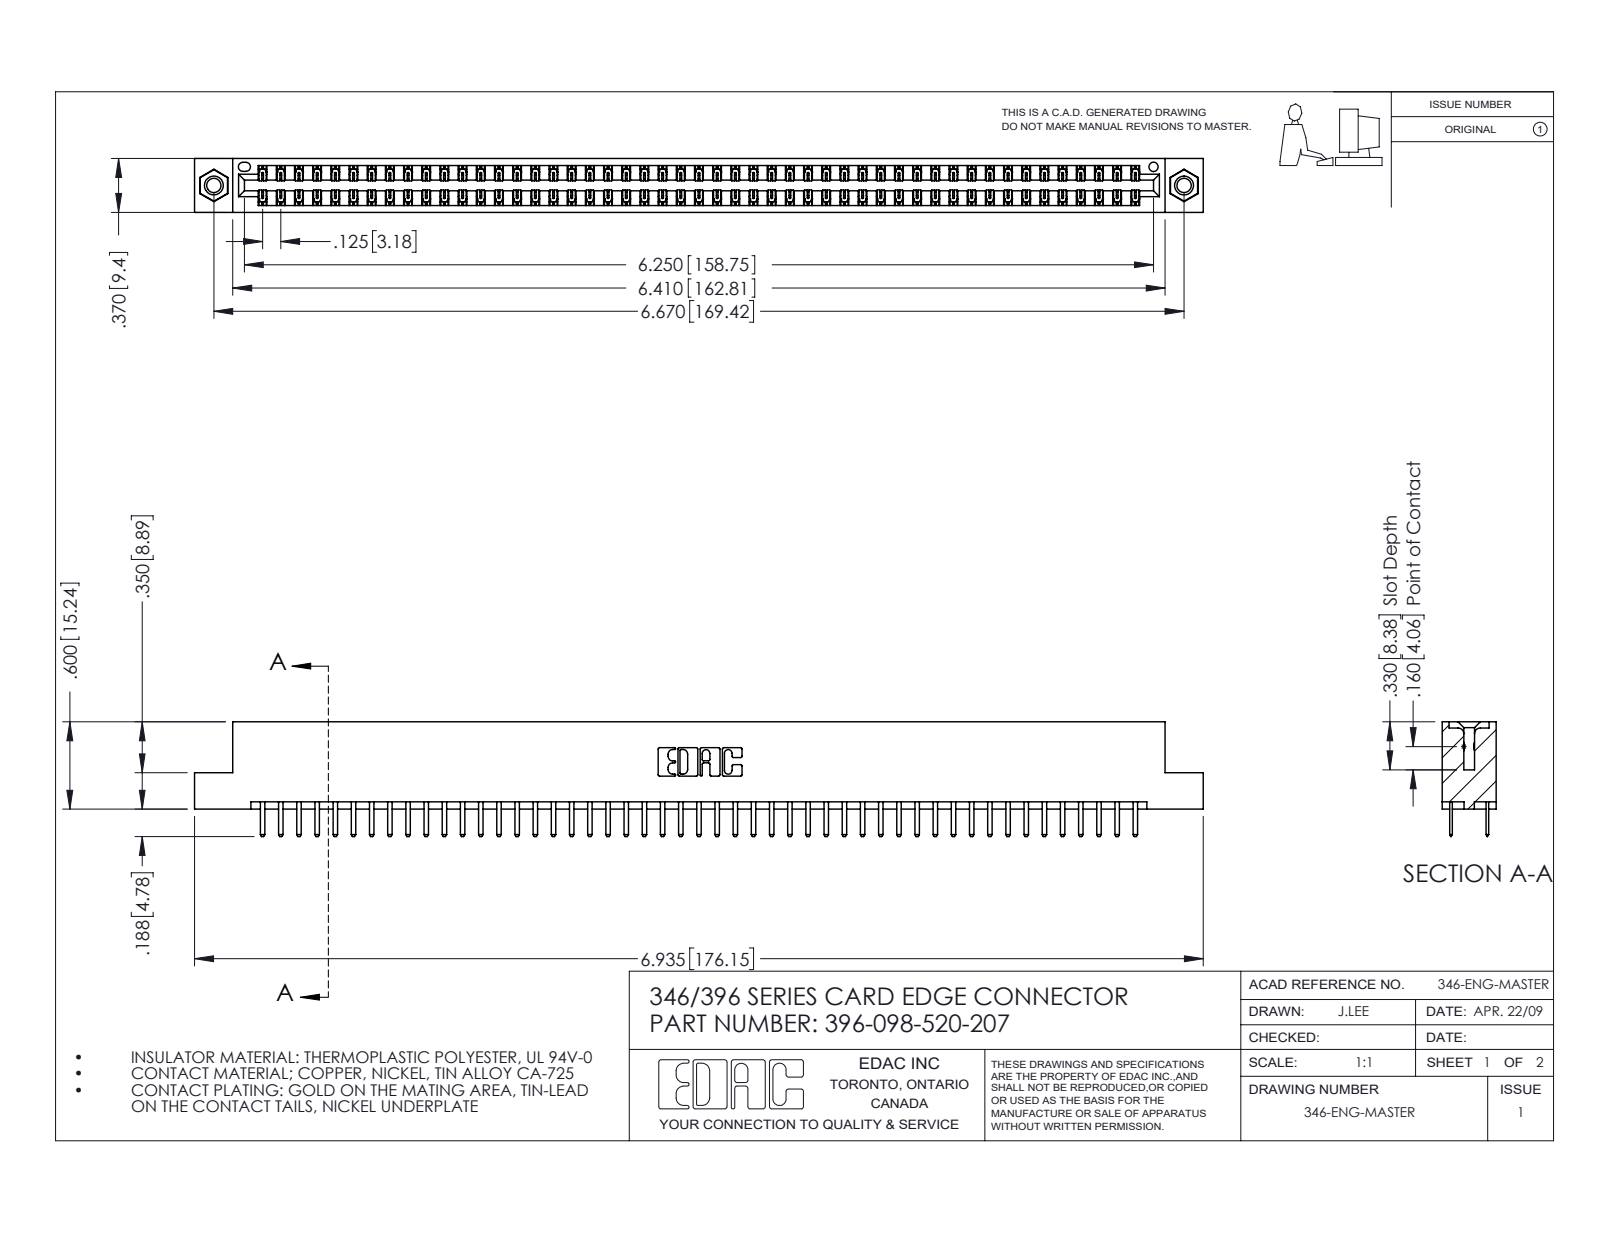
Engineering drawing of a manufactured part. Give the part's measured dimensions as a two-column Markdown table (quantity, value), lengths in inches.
| quantity | value |
| --- | --- |
| part name | 346 Part_Flush Mounting Lugs - 0.156 Dia-TI; 396-098-520-207; 345-250-001_345-250-005-103; 345-292-001_345-293-120 |
| STEP written by | SolidWorks 2016 (CONFIG_CONTROL_DESIGN) |
| units | inches |
| bodies | 101 solids, 5670 faces (3734 planar, 1920 cylindrical, 16 other) |
| overall size | 6.935 × 0.788 × 0.37 |
| volume | 1.048 in³ |
| surface area | 36.66 in² |
| round holes (diameter × count) | 0.098 × 2, 0.125 × 2, 0.156 × 2, 0.064 × 1 |
| round bosses / shafts (diameter × count) | 0.155 × 2 |
| partial cylindrical surfaces (radius × count) | 0.006 × 147, 0.01 × 102, 0.01 × 22, 0.007 × 6, 0.031 × 6, 0.026 × 3, 0.014 × 2, 0.022 × 2 |
| main face-to-face distances | 0.048, 0.322, 0.25, 0.37, 0.275, 0.072, 0.298, 0.025, 0.148, 0.222 |
| hole center spacings | 0.246, 6.461, 6.67 |
